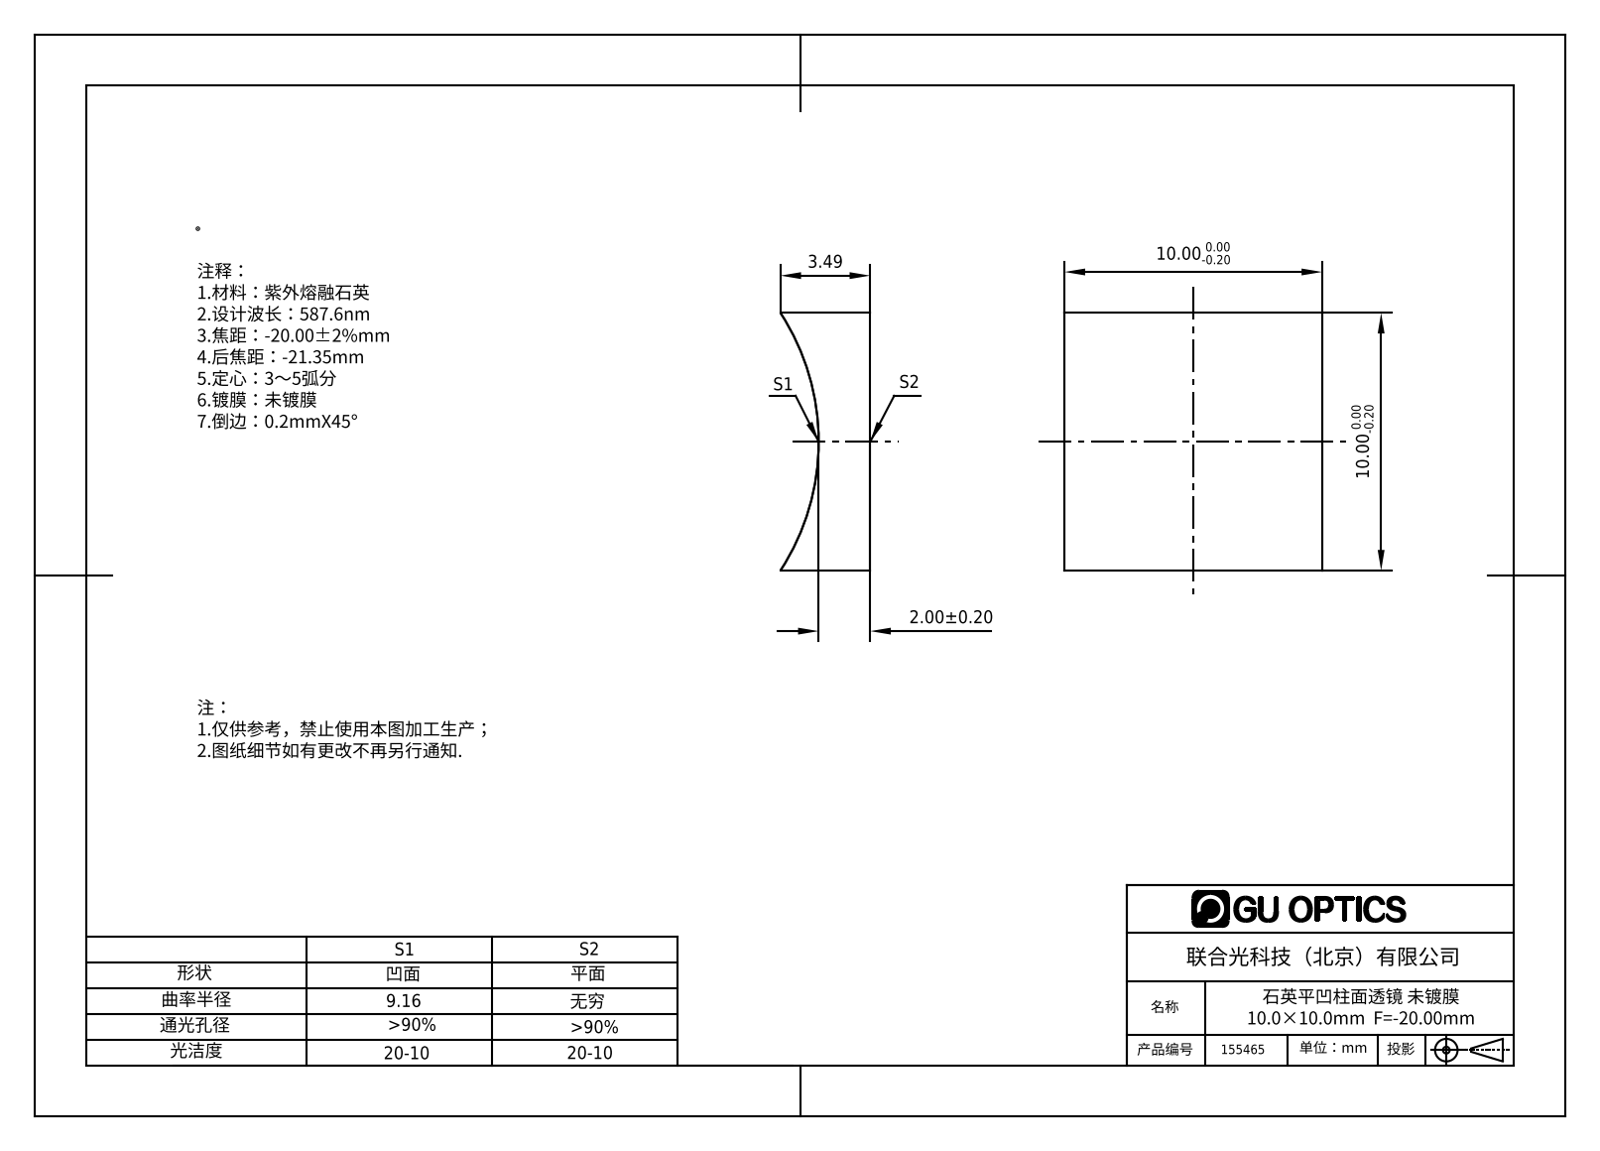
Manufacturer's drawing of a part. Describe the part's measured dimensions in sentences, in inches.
The part is named "155465". Its 3-D file was written by "SolidWorks 2016 (AUTOMOTIVE_DESIGN)". It is 1 solid with 6 faces: 5 planar, 1 cylindrical and 0 other. Overall it measures 0.394 by 0.394 by 0.137 inches. Its volume is 0.015 cubic inches and its surface area 0.504 square inches. Partial cylindrical surfaces (rounded edges, fillets, slot ends): 1 of radius 0.361. The main face-to-face distances are 0.394.
